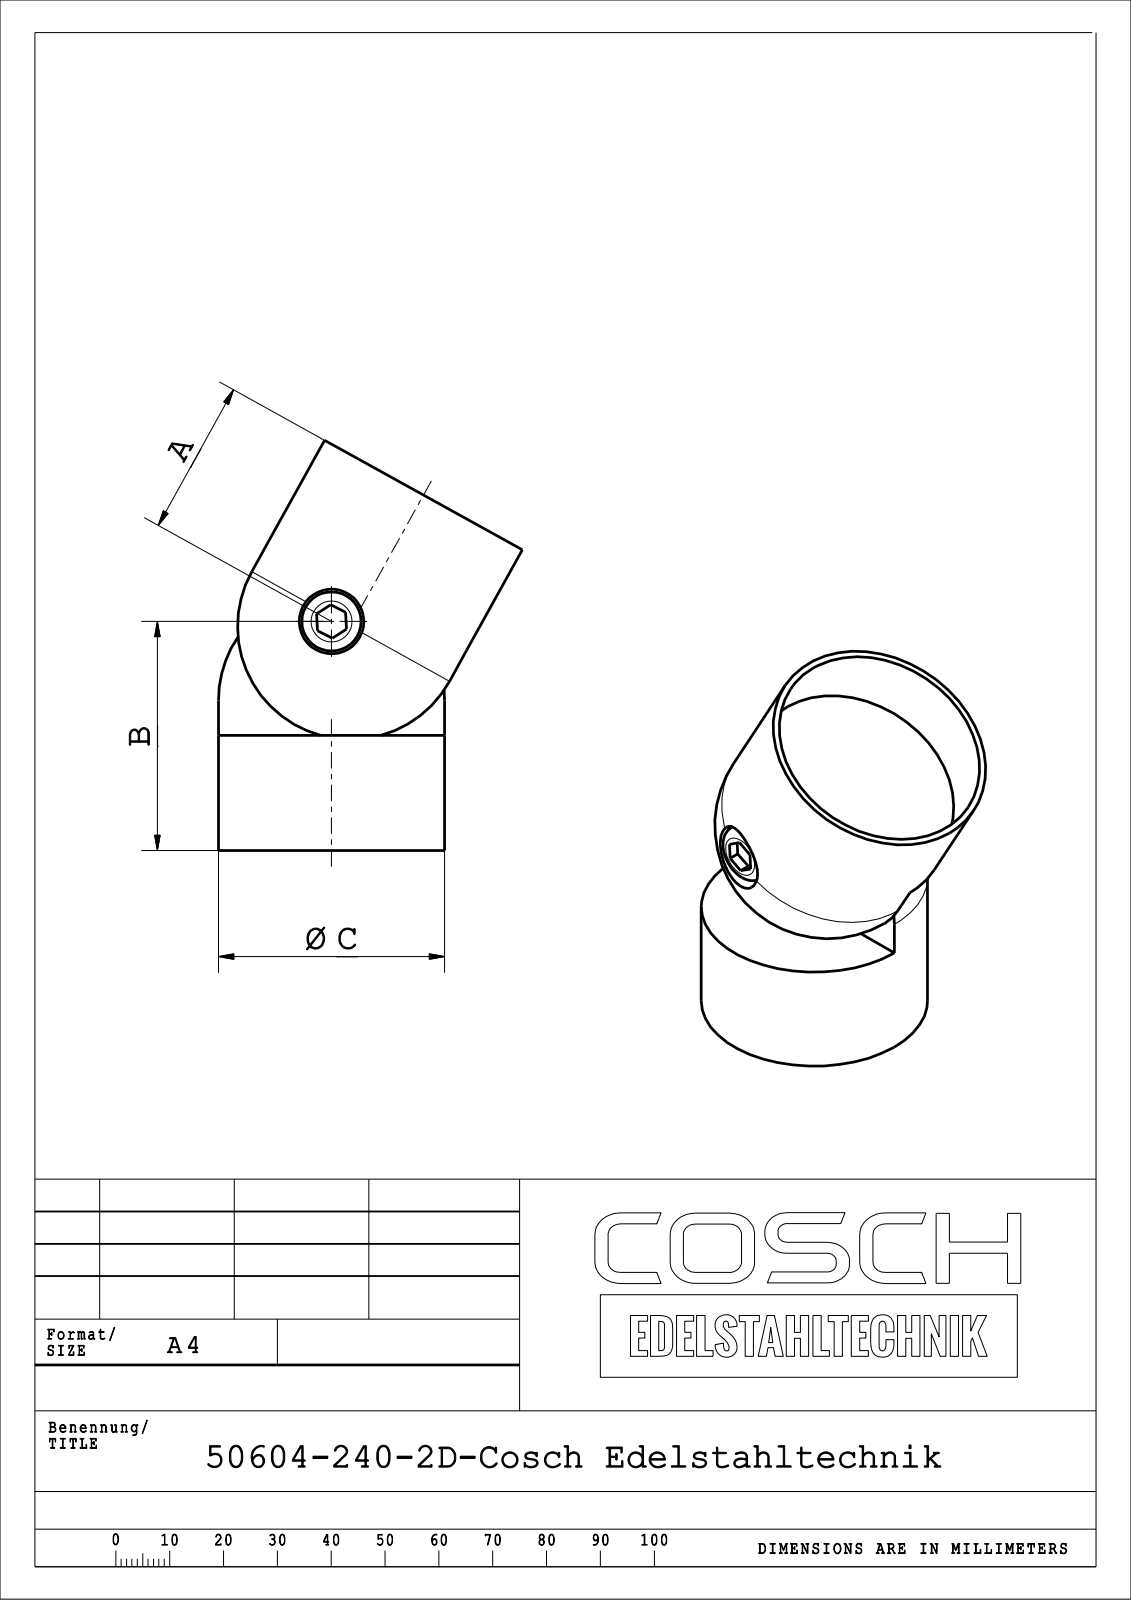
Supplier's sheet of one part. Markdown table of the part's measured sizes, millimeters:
| quantity | value |
| --- | --- |
| part name | Goge239860DCck8x |
| STEP written by | SIEMENS PLM Software NX 11.0 (AUTOMOTIVE_DESIGN) |
| units | millimeters |
| bodies | 2 solids, 26 faces (17 planar, 6 cylindrical, 3 other) |
| overall size | 76.23 × 56.45 × 42 |
| volume | 53 008 mm³ |
| surface area | 19 050 mm² |
| round holes (diameter × count) | 39.6 × 2, 12 × 1 |
| round bosses / shafts (diameter × count) | 42 × 2, 11 × 1 |
| main face-to-face distances | 7.4, 14, 21.4, 21.41, 14.01, 17.5, 2, 19.5, 5.4, 2.5 |
